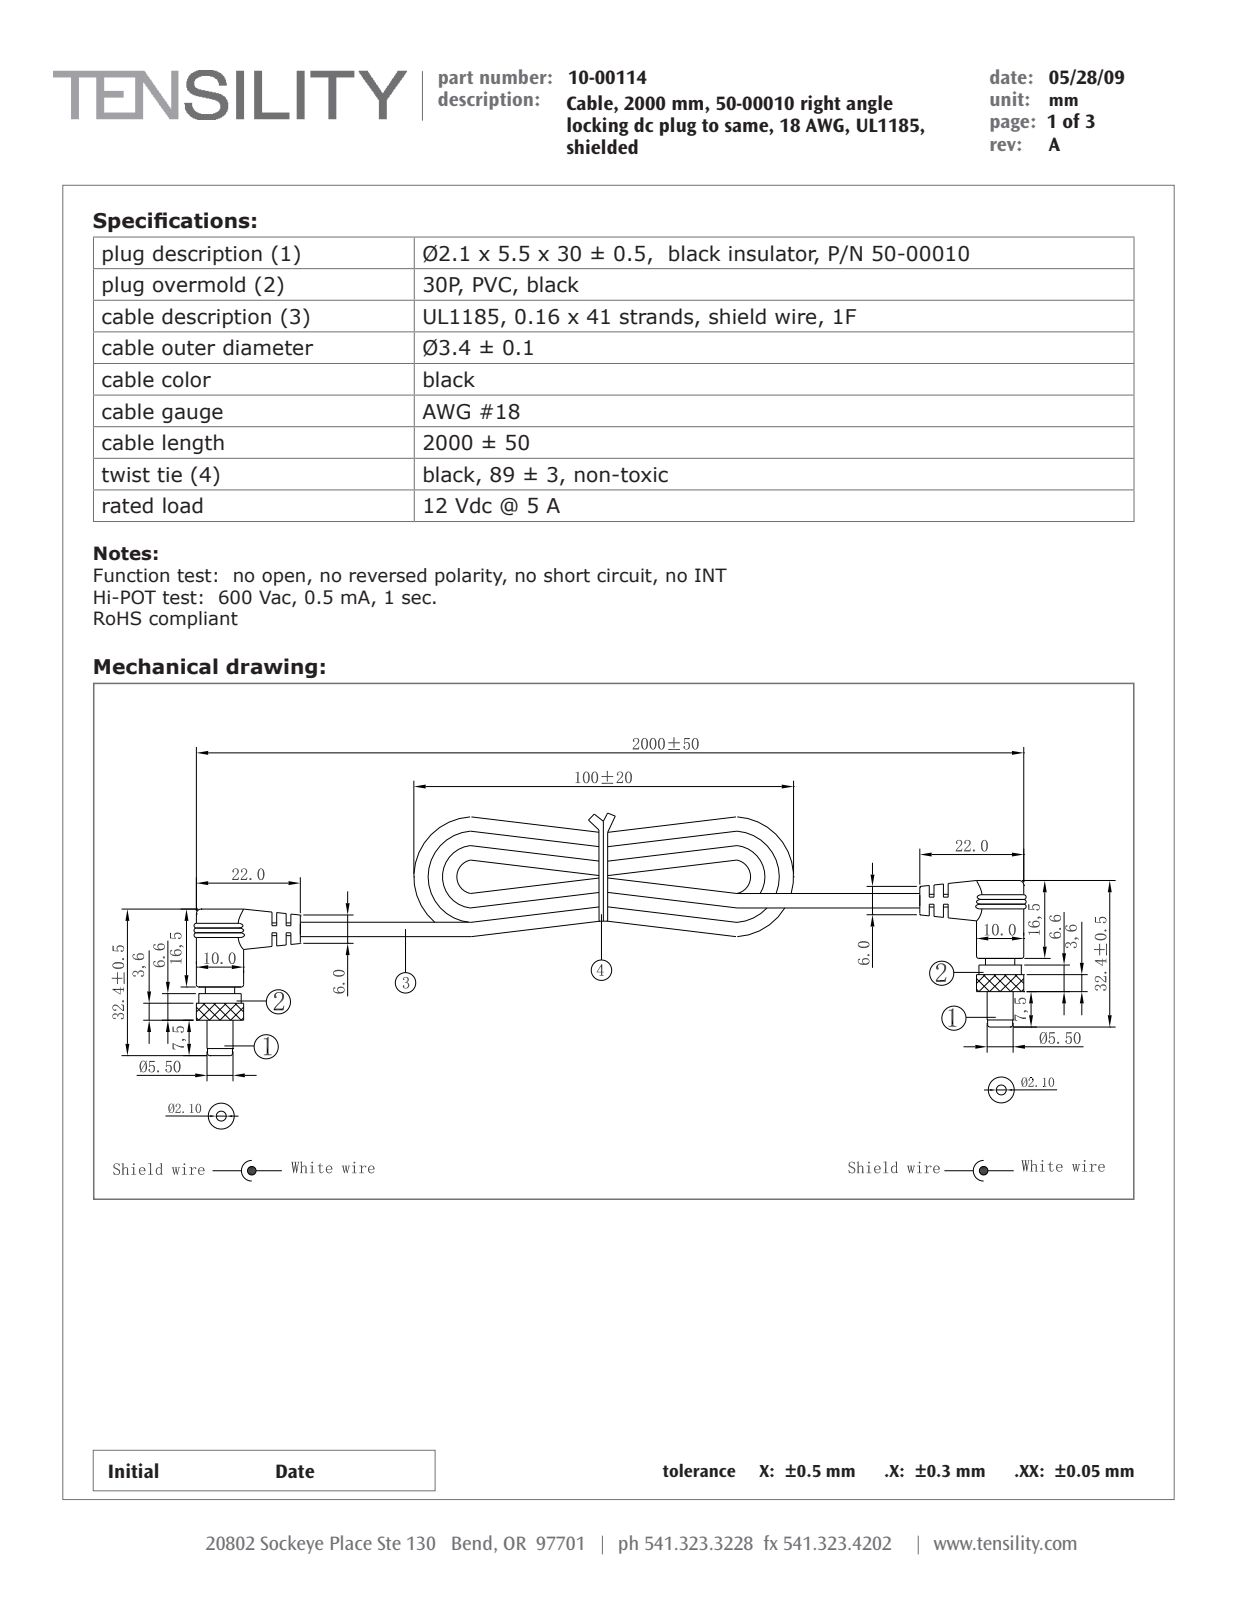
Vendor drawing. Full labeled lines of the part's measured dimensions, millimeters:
Part name (STEP PRODUCT): 50-00010 shell; 24-00017; 10-00114; 50-00010 shell 2 (+6 more)
STEP written by: SolidWorks 2015 (CONFIG_CONTROL_DESIGN)
Units: millimetres
Bodies: 98 solids, 3892 faces (1410 planar, 758 cylindrical, 1724 other)
Overall size (bounding box): 183 × 32.4 × 11
Volume: 6 227 mm³ · Surface area: 18 672 mm²
Round holes (diameter × count): ⌀1.6 ×2, ⌀2.1 ×2, ⌀2.16 ×2, ⌀2.6 ×2, ⌀2.85 ×2, ⌀3.85 ×2, ⌀5.04 ×2, ⌀5.44 ×2, ⌀5.5 ×2, ⌀5.65 ×2, ⌀6.4 ×2, ⌀7.25 ×2
Round bosses / shafts (diameter × count): ⌀11 ×2, ⌀10 ×2, ⌀7 ×2, ⌀6.2 ×2, ⌀6 ×2, ⌀5.48 ×2, ⌀5.3 ×2, ⌀8.5 ×1
Partial cylindrical surfaces — rounded edges, fillets, slot ends (radius × count): R0.75 ×4
Main face-to-face distances: 3, 1, 2, 16.5, 8.4, 24.9, 146, 143, 1.8, 6.6
Hole centre spacings: 172
